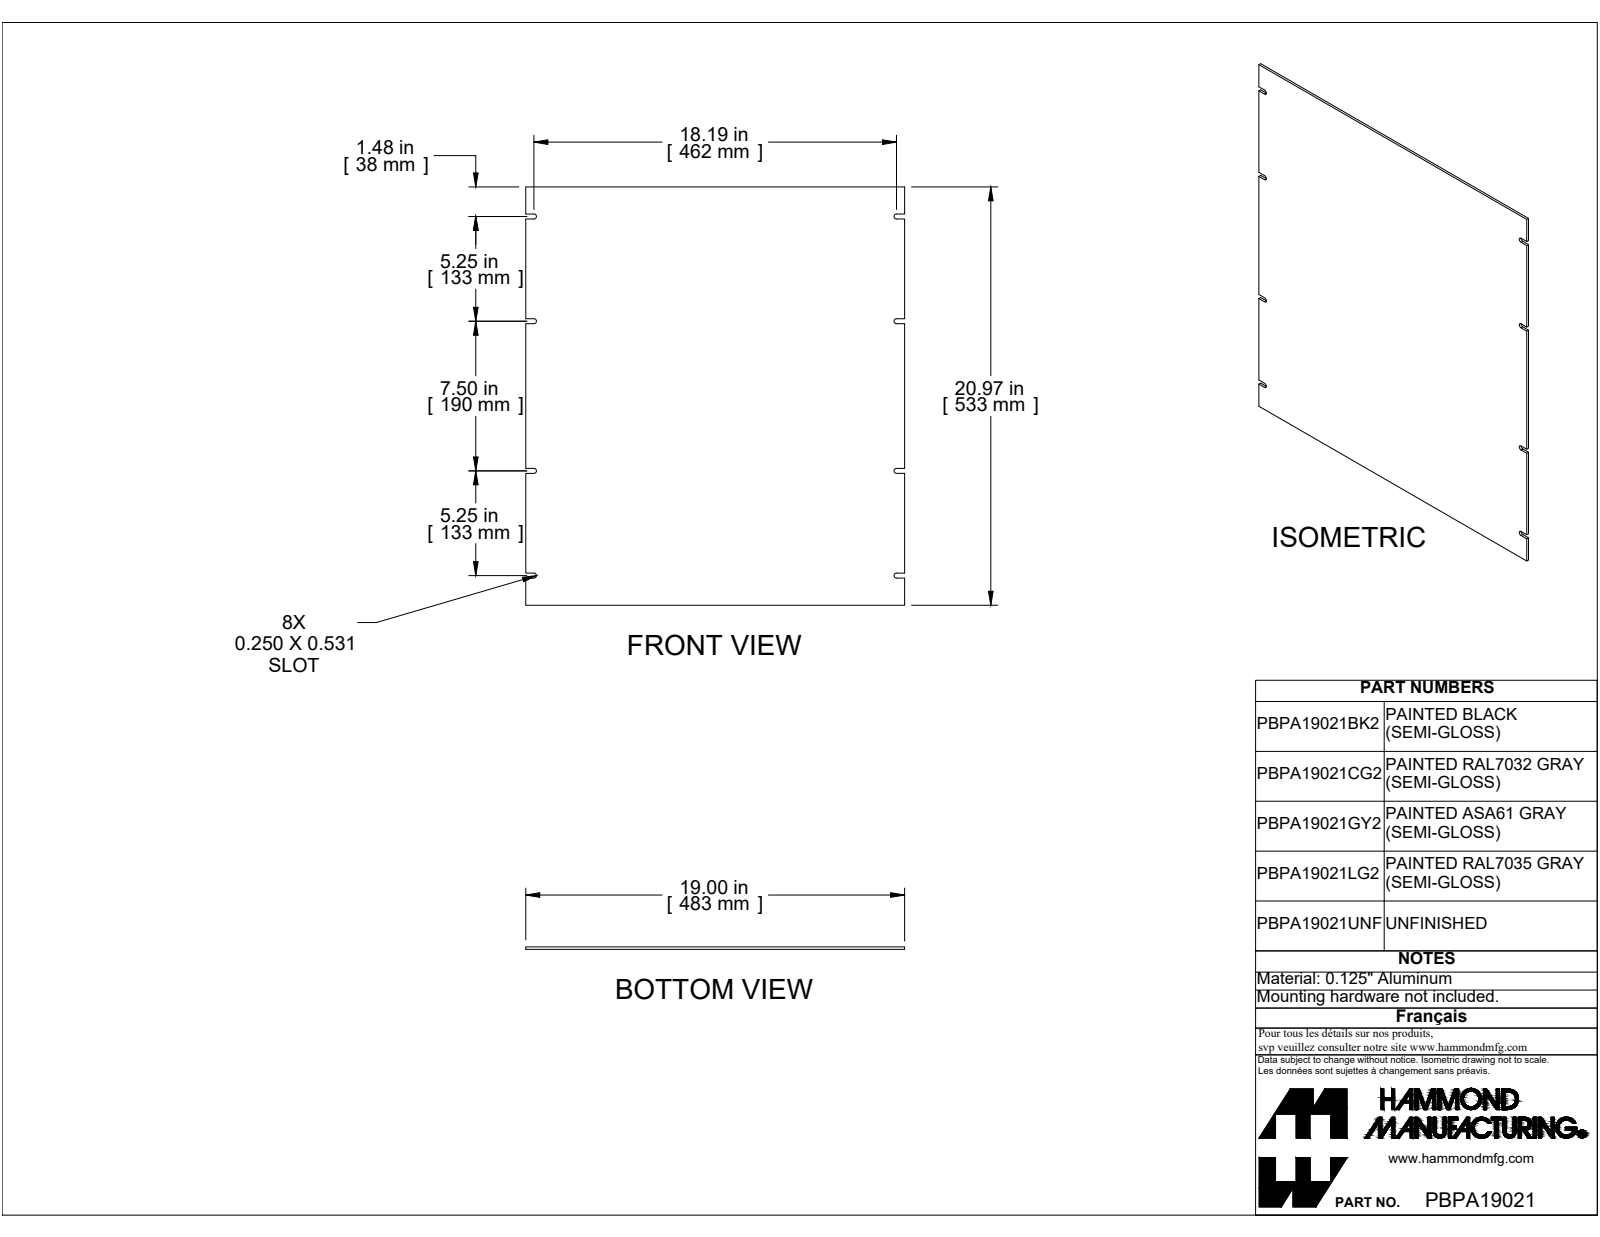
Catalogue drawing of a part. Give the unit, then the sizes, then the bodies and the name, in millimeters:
Units: millimetres
Overall size (bounding box): 532.6 × 482.6 × 3.2
Partial cylindrical surfaces — rounded edges, fillets, slot ends (radius × count): R3.2 ×8
Main face-to-face distances: 3.2, 482.6, 532.6, 6.4, 34.5, 40.9, 491.7, 498.1, 133.4, 323.9
Volume: 813 900 mm³ · Surface area: 519 800 mm²
Bodies: 1 solid, 38 faces (30 planar, 8 cylindrical, 0 other)
Part name (STEP PRODUCT): PBPA19021UNF
STEP written by: SolidWorks 2019 (CONFIG_CONTROL_DESIGN)
